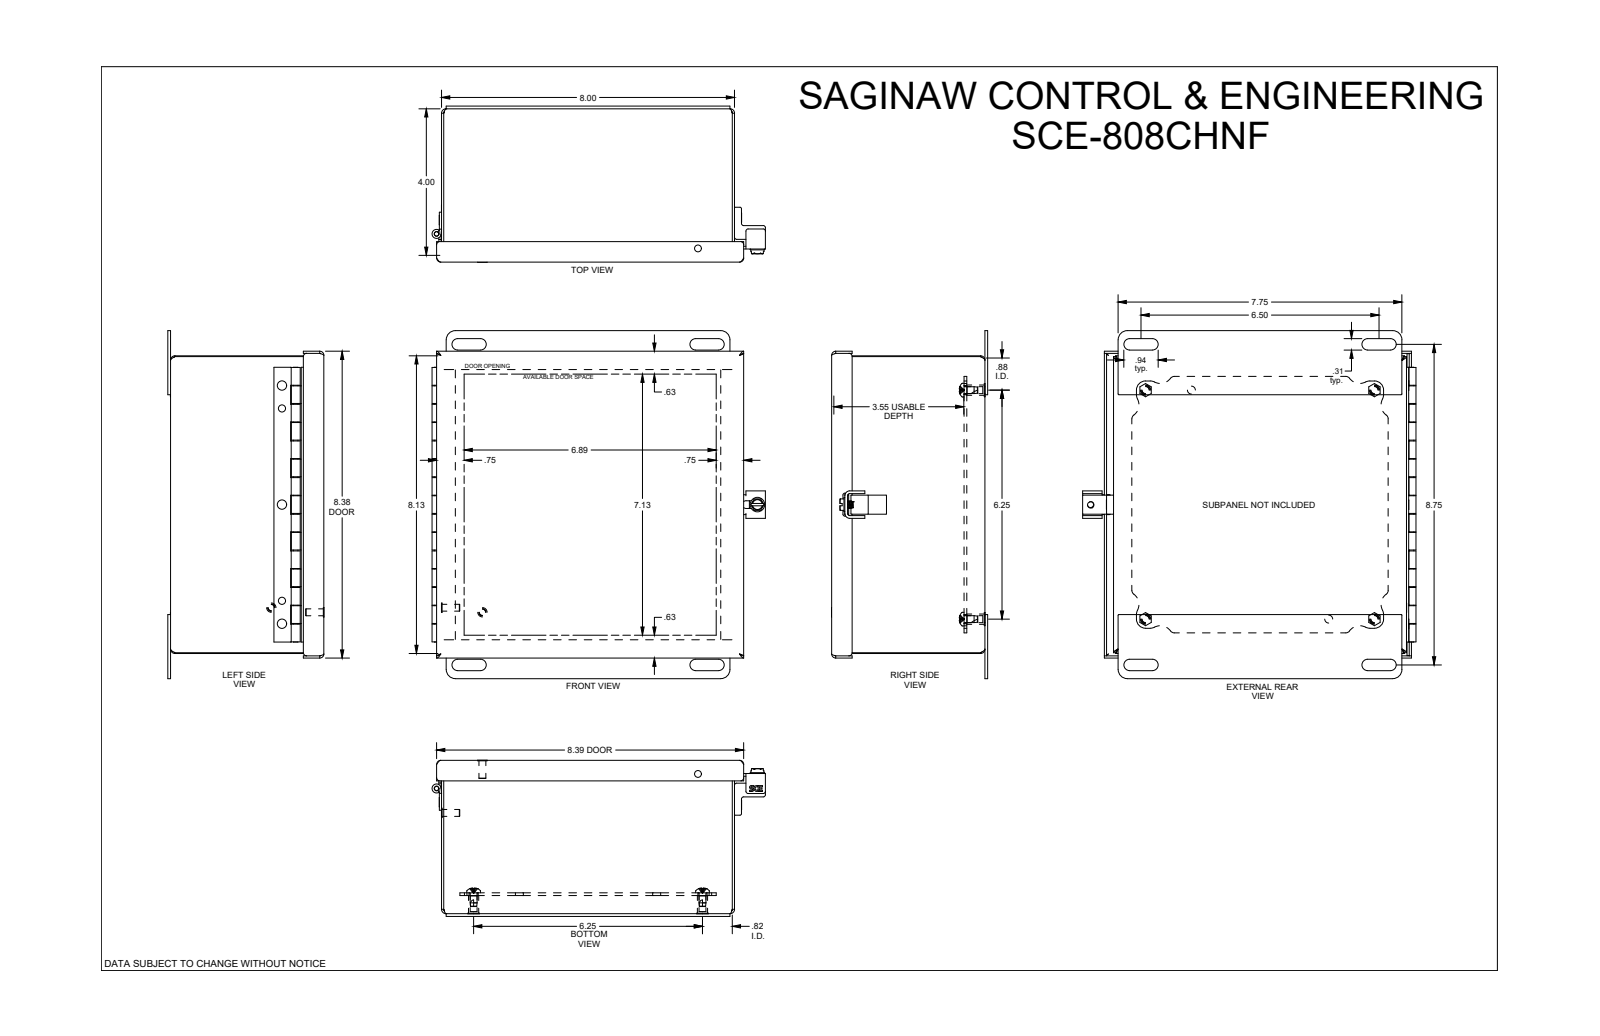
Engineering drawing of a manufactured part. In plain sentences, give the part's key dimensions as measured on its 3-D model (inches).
The part is named "SCE-808CHNF". Its 3-D file was written by "SolidWorks 2019 (CONFIG_CONTROL_DESIGN)". It is 0 solids with 1091 faces: 500 planar, 293 cylindrical and 298 other. Overall it measures 9.5 by 9.104 by 4.265 inches. Round holes: 8 of diameter 0.19, 6 of diameter 0.193, 4 of diameter 0.25, 4 of diameter 0.281, 2 of diameter 0.193, 2 of diameter 0.218, 1 of diameter 0.126, 1 of diameter 0.156, 1 of diameter 0.187, 1 of diameter 0.266. Round bosses or shafts: 11 of diameter 0.188, 6 of diameter 0.256, 4 of diameter 0.373, 4 of diameter 0.28, 1 of diameter 0.396, 1 of diameter 0.246, 1 of diameter 0.123. Partial cylindrical surfaces (rounded edges, fillets, slot ends): 56 of radius 0.01, 16 of radius 0.25, 13 of radius 0.06, 8 of radius 0.052, 8 of radius 0.112, 8 of radius 0.125, 8 of radius 0.156, 8 of radius 0.344. The main face-to-face distances are 0.06, 0.06, 4.125, 4.185, 7.94, 4.065, 4.125, 0.075, 3.63, 0.57. The hole center spacings are 6.25, 1.25, 3.25, 3.251, 5, 6.374, 8.004, 8.356.
